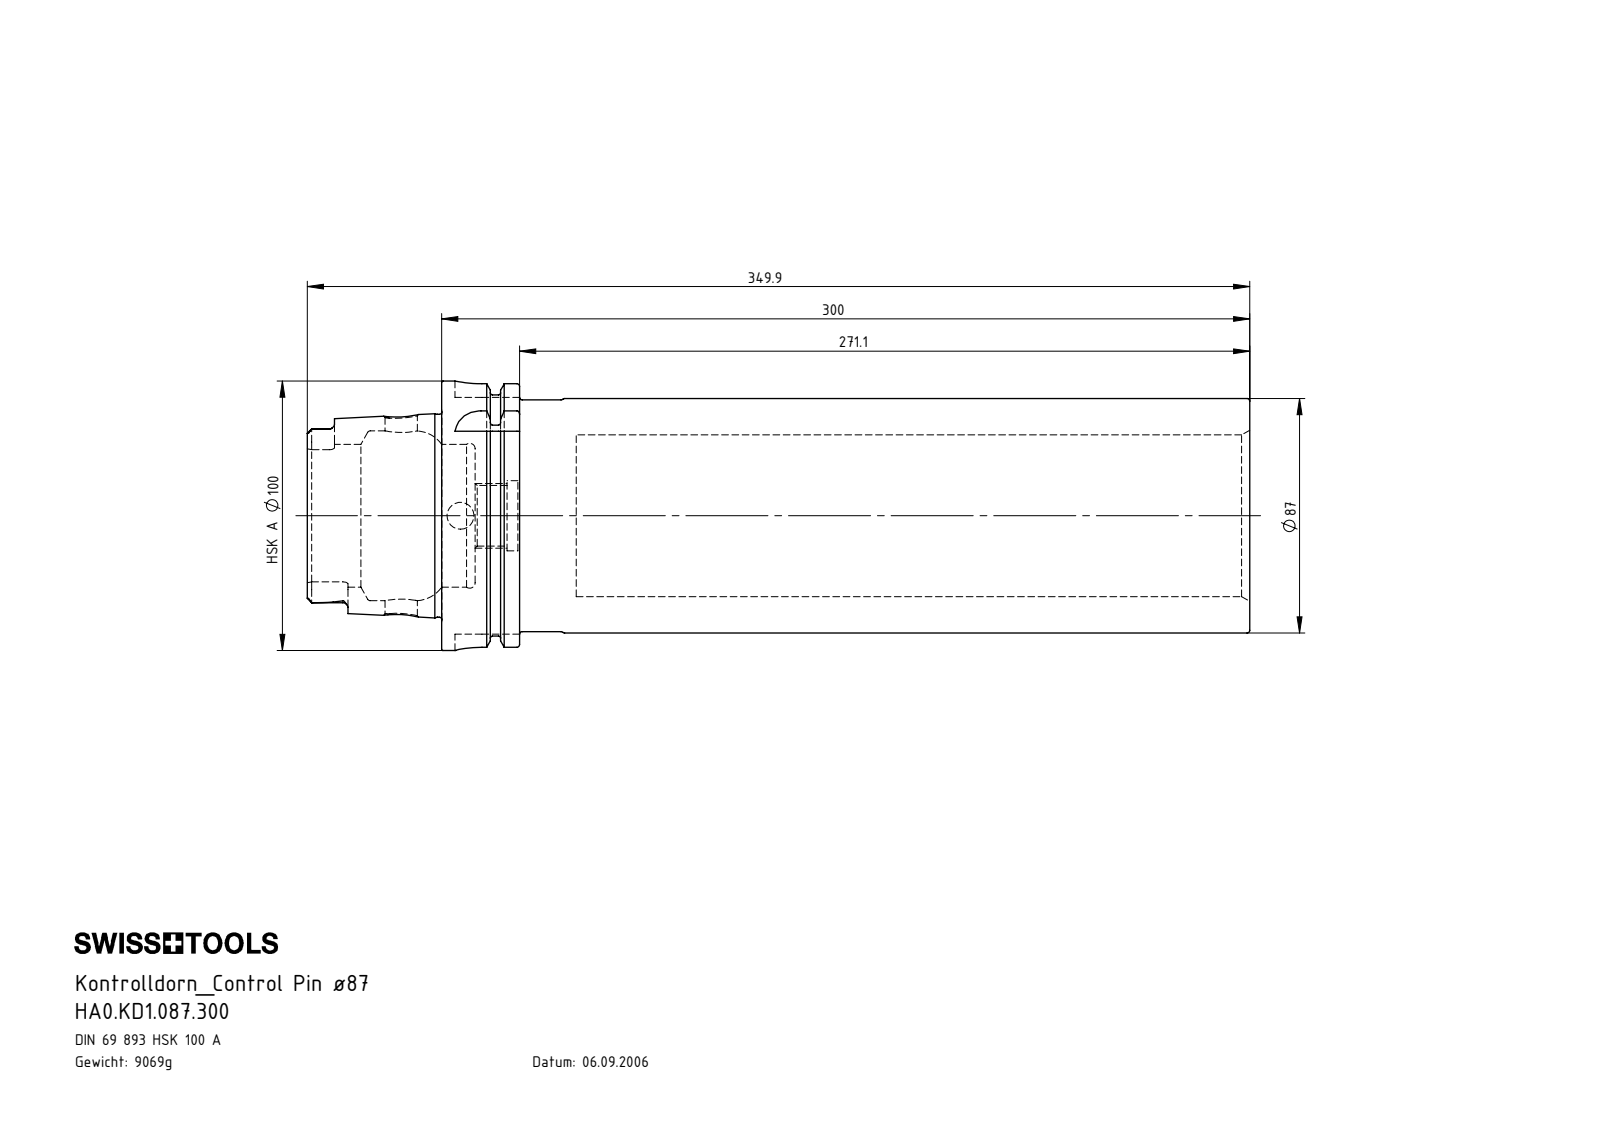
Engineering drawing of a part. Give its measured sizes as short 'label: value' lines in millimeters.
name: HA0.KD1.087.300
written by: SolidWorks 2017 (AUTOMOTIVE_DESIGN)
unit: mm
bodies: 1 solid, 159 faces (42 planar, 48 cylindrical, 69 other)
size: 349.9 × 100 × 100
volume: 1 155 000 mm³; area: 170 494 mm²
holes: 1× ⌀10, 1× ⌀12, 1× ⌀22.5, 1× ⌀26, 1× ⌀53, 1× ⌀60, 1× ⌀63
bosses: 1× ⌀100, 1× ⌀91.95, 1× ⌀87, 1× ⌀86, 1× ⌀75.26
rounds: 6× R1.9, 4× R4.88, 4× R10
face distances: 50, 300, 250, 12.45, 37.55, 287.55, 28.95, 16.5, 21.05, 271.05
